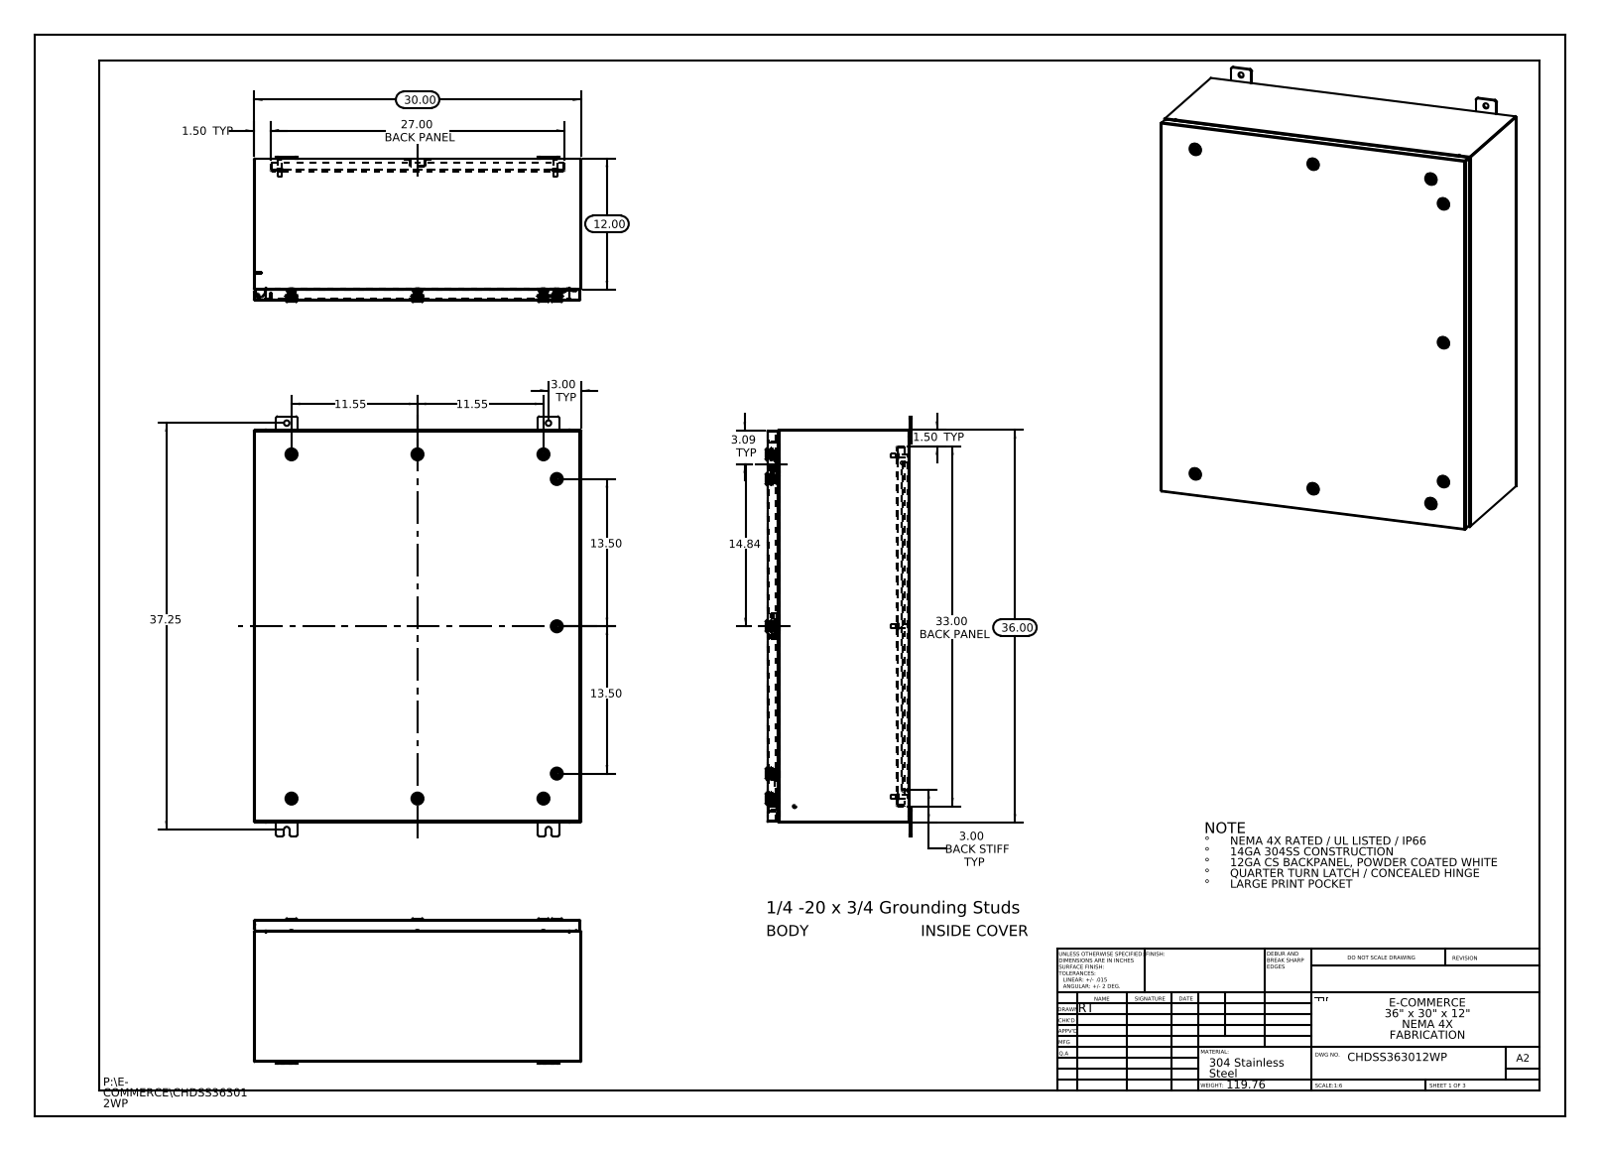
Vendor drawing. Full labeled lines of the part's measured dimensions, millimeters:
Part name (STEP PRODUCT): CHDSS363012WP; Screw-221320-IB-Industrilas_Screw-221320-IB-Industrilas; CHDSS363012WP Mounting Feet; CHDSS363012WP Mounting Studs (+8 more)
STEP written by: SolidWorks 2013 (CONFIG_CONTROL_DESIGN)
Units: millimetres
Bodies: 76 solids, 7956 faces (2284 planar, 2478 cylindrical, 3194 other)
Overall size (bounding box): 977.9 × 762 × 339.2
Volume: 6 951 000 mm³ · Surface area: 6 820 000 mm²
Round holes (diameter × count): ⌀12.7 ×10, ⌀5 ×9, ⌀10 ×9, ⌀10.2 ×9, ⌀16 ×9, ⌀20 ×9, ⌀3.5 ×2, ⌀5.4 ×1
Round bosses / shafts (diameter × count): ⌀6 ×11, ⌀28 ×9, ⌀19.8 ×9, ⌀15.9 ×9, ⌀15.5 ×9, ⌀13.5 ×9, ⌀10 ×9, ⌀2.9 ×9
Partial cylindrical surfaces — rounded edges, fillets, slot ends (radius × count): R0.2 ×297, R3 ×297, R0.7 ×108, R0.5 ×36, R5 ×36, R0.3 ×26, R4.8 ×24, R2.2 ×22
Main face-to-face distances: 1.9, 1.9, 330.5, 328.5, 328.6, 326.7, 2.6, 25.4, 27.3, 301.3
Hole centre spacings: 293.4, 396.9, 754.2, 853.4, 641.4, 801.4, 47.2, 77.9
